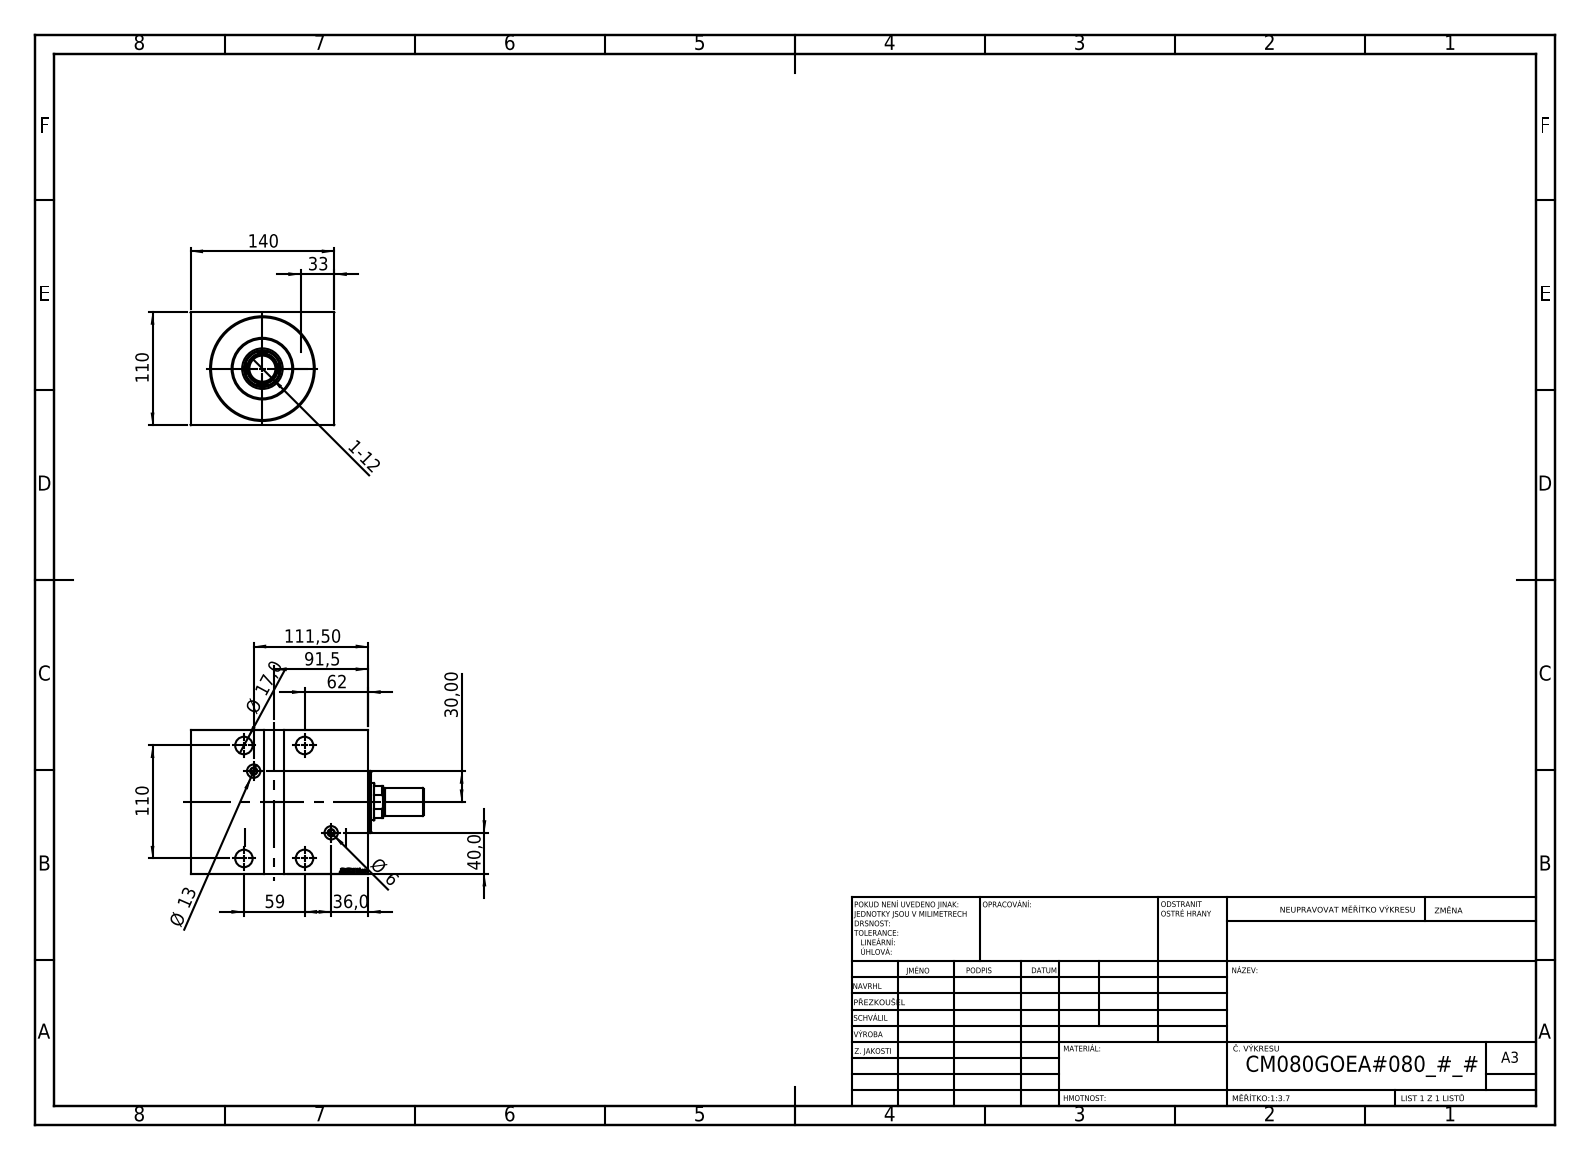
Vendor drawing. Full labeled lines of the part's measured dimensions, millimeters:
Part name (STEP PRODUCT): V450CM_G_VCP; V450CM_MALE_METRIC; V450CM_G_Body; V450CM_VC_G (+1 more)
STEP written by: SolidWorks 2019 (CONFIG_CONTROL_DESIGN)
Units: millimetres
Bodies: 6 solids, 910 faces (446 planar, 60 cylindrical, 404 other)
Overall size (bounding box): 227 × 140 × 110
Volume: 2 192 000 mm³ · Surface area: 245 316 mm²
Round holes (diameter × count): ⌀17 ×4, ⌀25 ×4, ⌀6 ×2, ⌀13 ×2, ⌀25.5 ×1, ⌀36 ×1, ⌀39.5 ×1, ⌀80 ×1, ⌀82 ×1, ⌀100 ×1
Round bosses / shafts (diameter × count): ⌀26 ×2, ⌀7 ×2, ⌀60 ×1, ⌀27 ×1, ⌀25 ×1
Partial cylindrical surfaces — rounded edges, fillets, slot ends (radius × count): R17.5 ×1
Main face-to-face distances: 110, 140, 5, 173, 21, 152, 168, 147, 79, 58
Hole centre spacings: 59, 110, 124.82, 26.74, 36.07, 55.45, 85.53, 88.6
